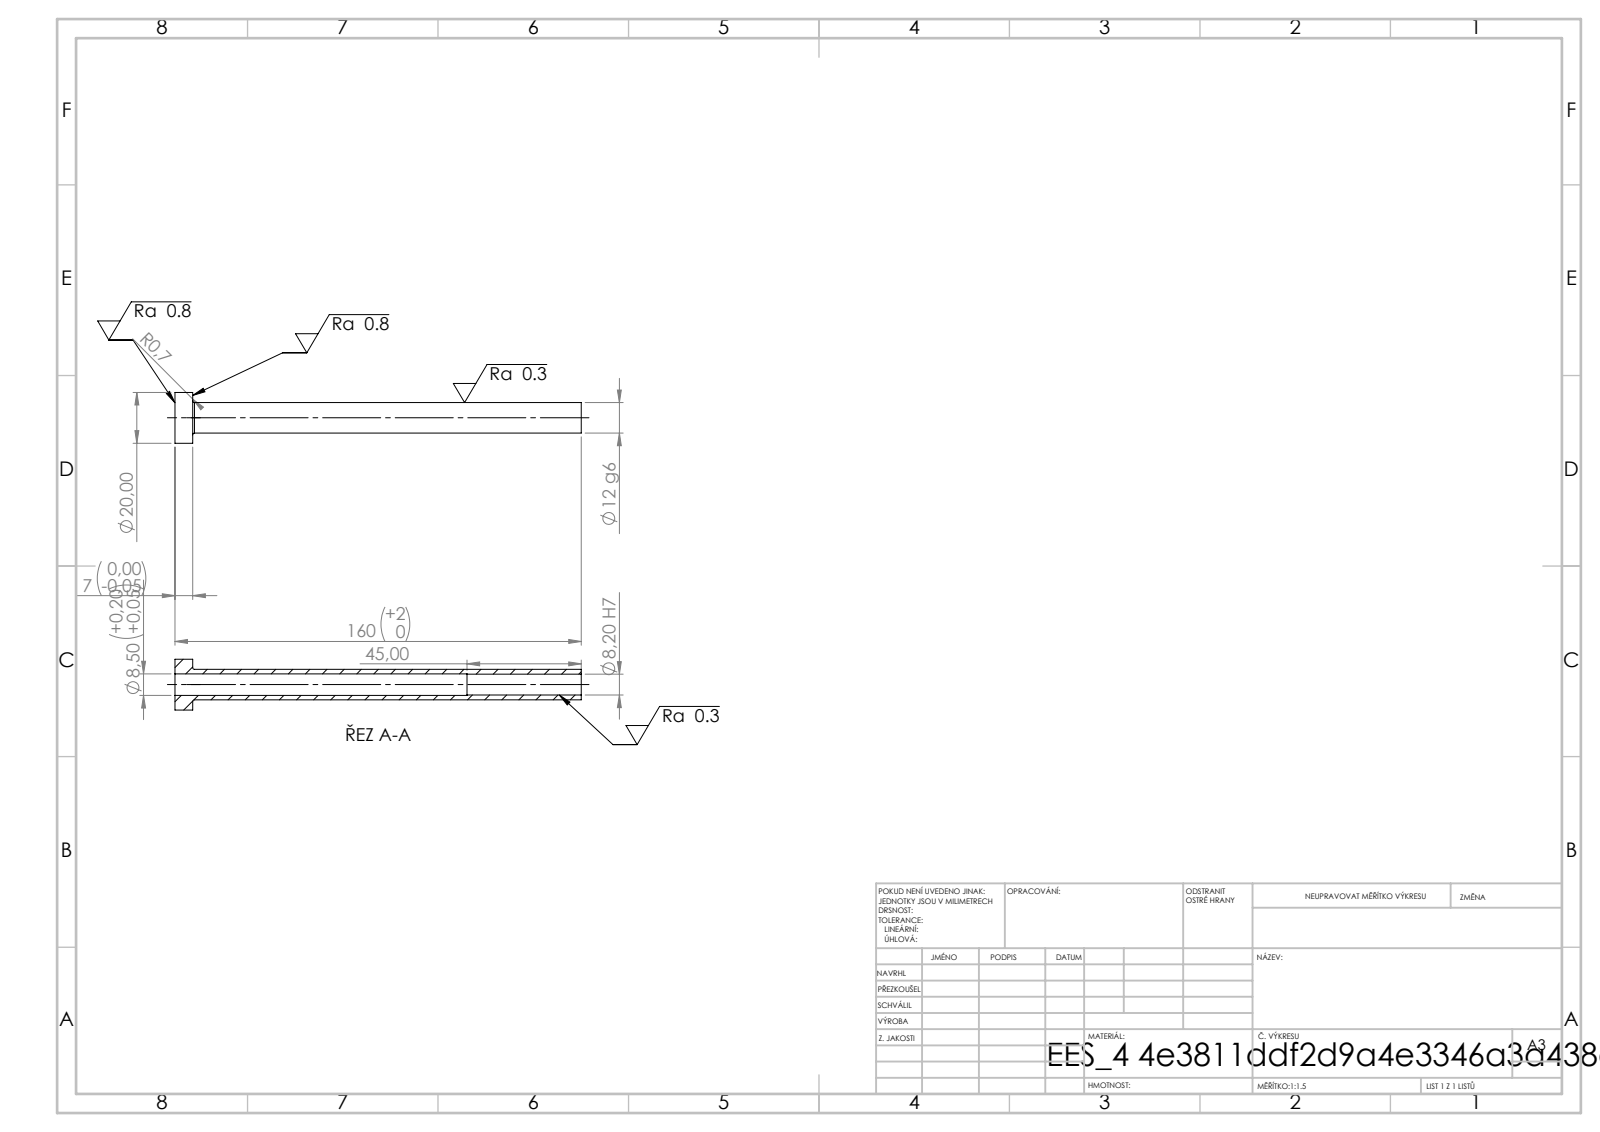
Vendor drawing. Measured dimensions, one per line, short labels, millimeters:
written by: SolidWorks 2019 (CONFIG_CONTROL_DESIGN)
unit: mm
bodies: 1 solid, 14 faces (4 planar, 8 cylindrical, 2 other)
size: 160 × 20 × 20
volume: 10 605 mm³; area: 10 950 mm²
holes: 1× ⌀8.2, 1× ⌀8.5
bosses: 1× ⌀20, 1× ⌀12
face distances: 7, 160, 153, 115, 108, 45
